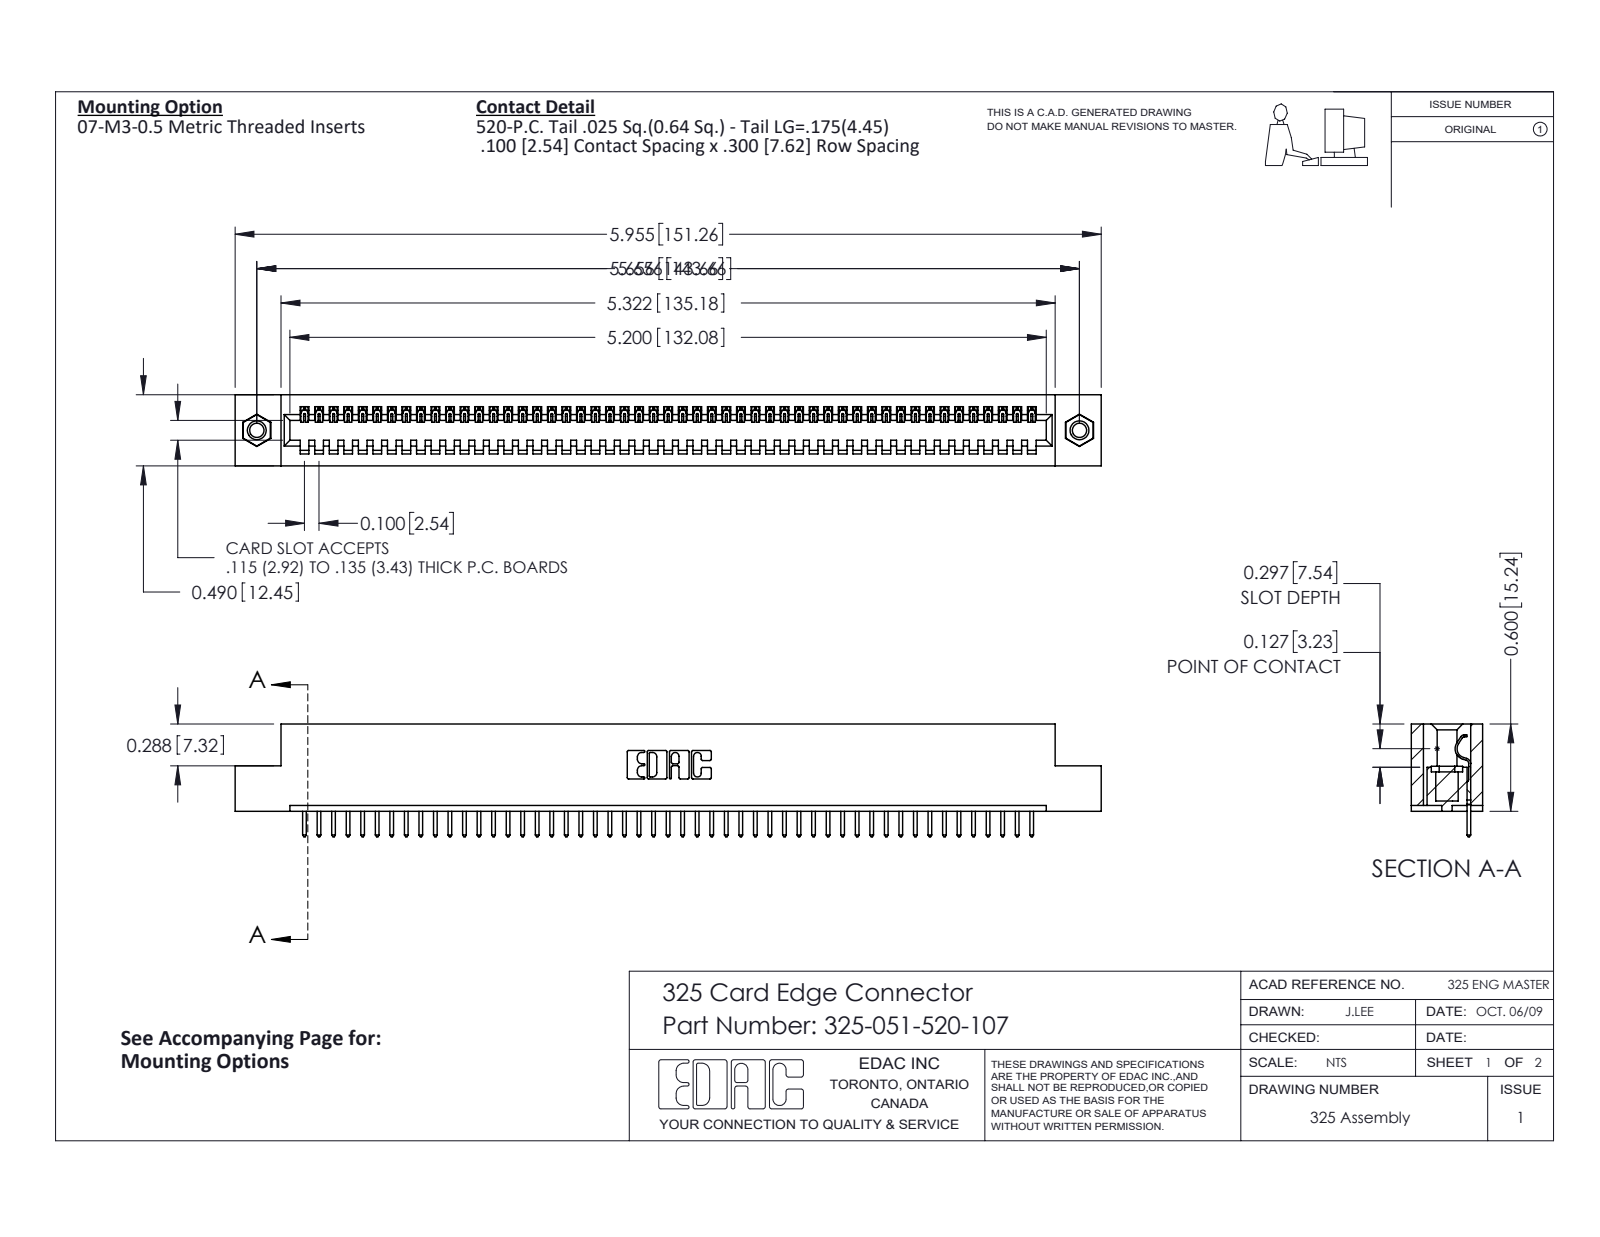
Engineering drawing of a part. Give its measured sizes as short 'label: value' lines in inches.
name: 325-292-001_325-293-120; 325 Part_TI; 325-051-520-107; 345-250-001_345-250-005-103
written by: SolidWorks 2016 (CONFIG_CONTROL_DESIGN)
unit: in
bodies: 54 solids, 3132 faces (2244 planar, 872 cylindrical, 16 other)
size: 5.955 × 0.775 × 0.49
volume: 1.167 in³; area: 31.84 in²
holes: 2× ⌀0.098, 2× ⌀0.125, 2× ⌀0.16
bosses: 2× ⌀0.155
rounds: 102× R0.006, 102× R0.01, 22× R0.01, 6× R0.007, 6× R0.031, 3× R0.026, 1× R0.014, 1× R0.022
face distances: 0.083, 0.407, 0.49, 0.3, 0.107, 0.383, 0.025, 0.325, 0.56, 0.263
hole spacings: 5.656
